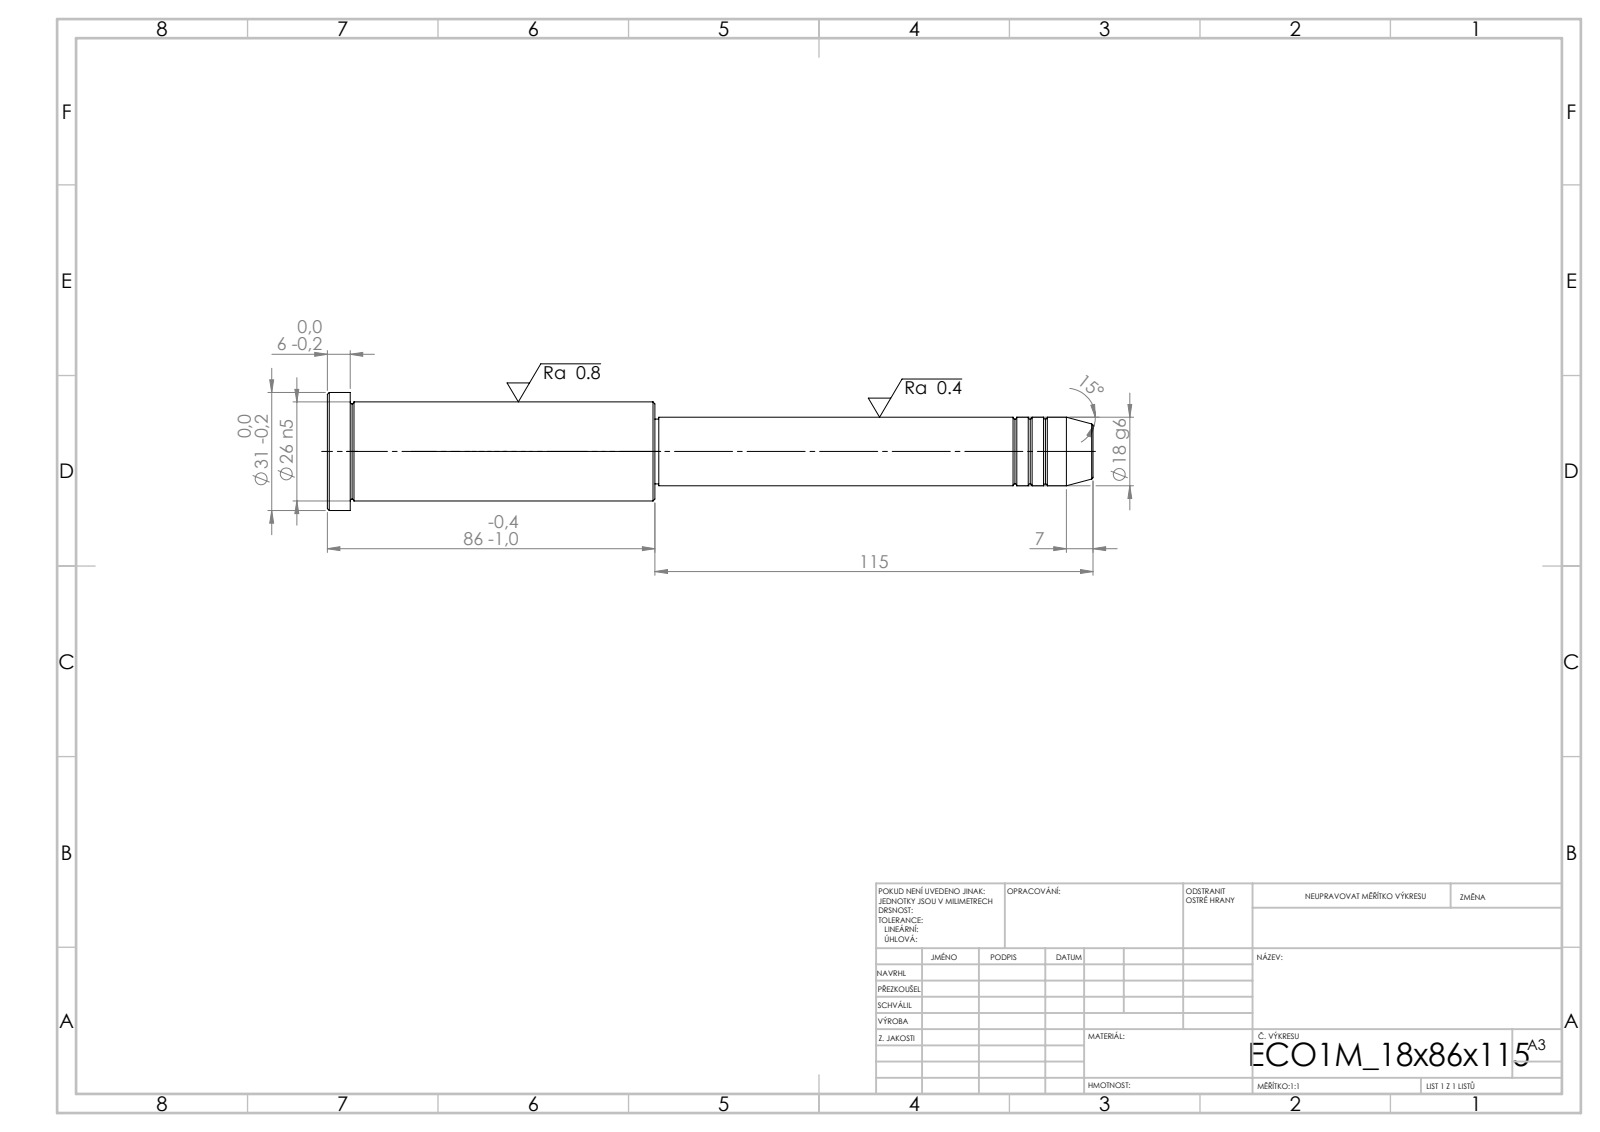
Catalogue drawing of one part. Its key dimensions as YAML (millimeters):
step_written_by: "SolidWorks 2019 (CONFIG_CONTROL_DESIGN)"
units: millimeters
bodies: {solids: 1, faces: 43, planar: 5, cylindrical: 14, other: 24}
overall_size: [201, 31, 31]
volume: 75774
surface_area: 15132
round_bosses_or_shafts:
  - {diameter: 31, count: 1}
  - {diameter: 26, count: 1}
  - {diameter: 18, count: 1}
  - {diameter: 17, count: 1}
face_to_face_distances: [86, 80, 6, 115, 195, 201, 114, 1, 81, 87]
